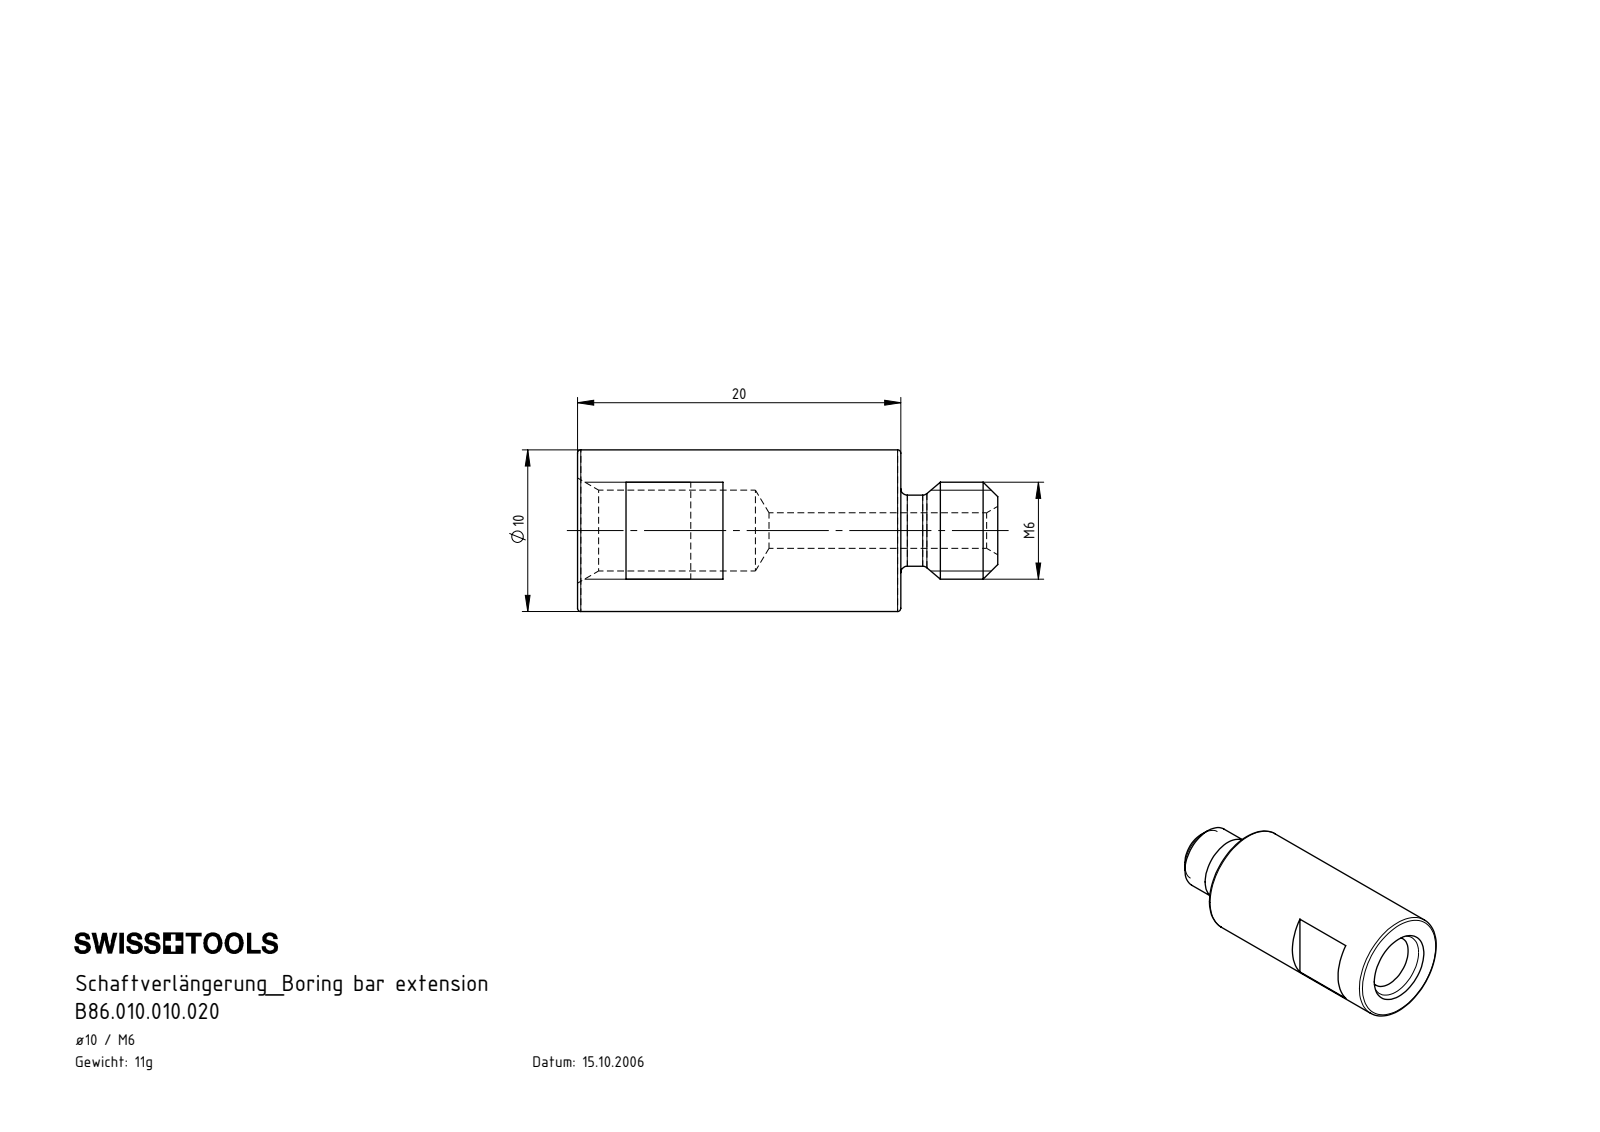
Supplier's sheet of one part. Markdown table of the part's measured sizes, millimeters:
| quantity | value |
| --- | --- |
| part name | B86.010.010.020 |
| STEP written by | SolidWorks 2022 (CONFIG_CONTROL_DESIGN) |
| units | millimeters |
| bodies | 1 solid, 37 faces (9 planar, 10 cylindrical, 18 other) |
| overall size | 26 × 10 × 10 |
| volume | 1 370 mm³ |
| surface area | 1 156 mm² |
| round holes (diameter × count) | 2.2 × 1, 5 × 1 |
| round bosses / shafts (diameter × count) | 10 × 1, 6 × 1, 4.4 × 1 |
| main face-to-face distances | 20, 8, 17, 6, 3, 11, 9, 23, 26 |
